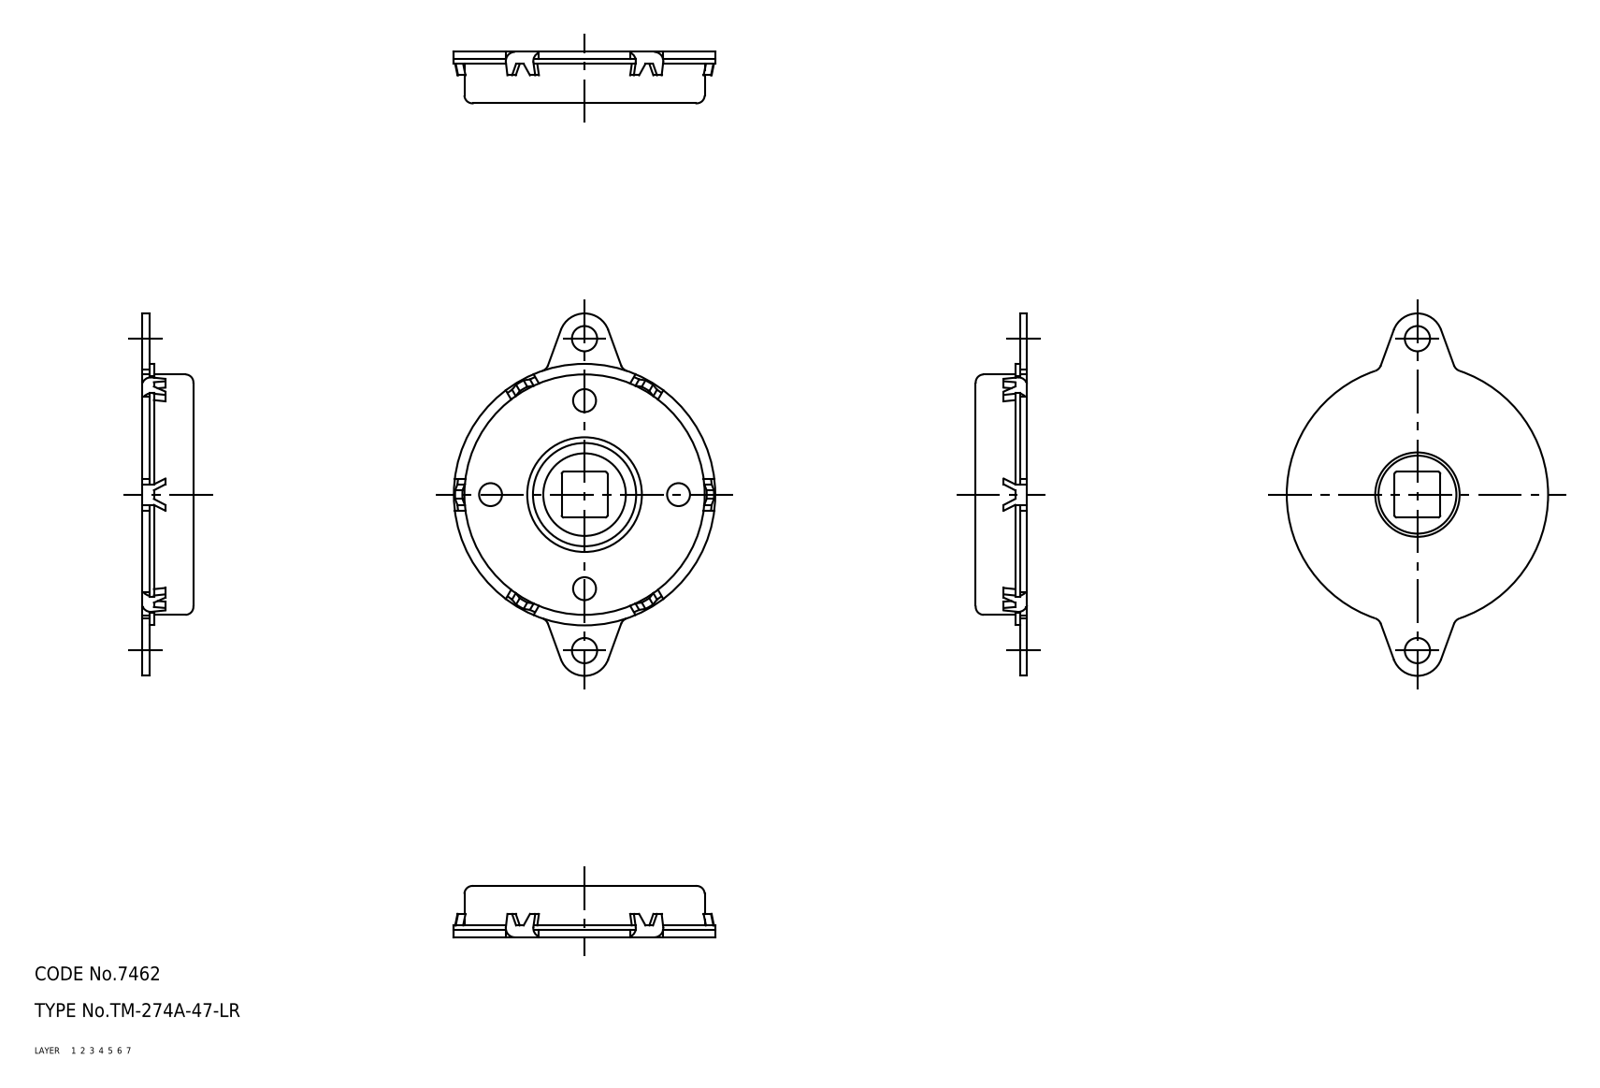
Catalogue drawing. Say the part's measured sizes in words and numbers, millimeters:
The part is named "inner ring; TM_274A_47_LR_508_36". Its 3-D file was written by "CADfix (AUTOMOTIVE_DESIGN)". It is 2 solids with 187 faces: 0 planar, 0 cylindrical and 187 other. Overall it measures 79 by 57 by 11.2 millimeters. Its volume is 23 226 cubic millimeters and its surface area 10 196 square millimeters.
